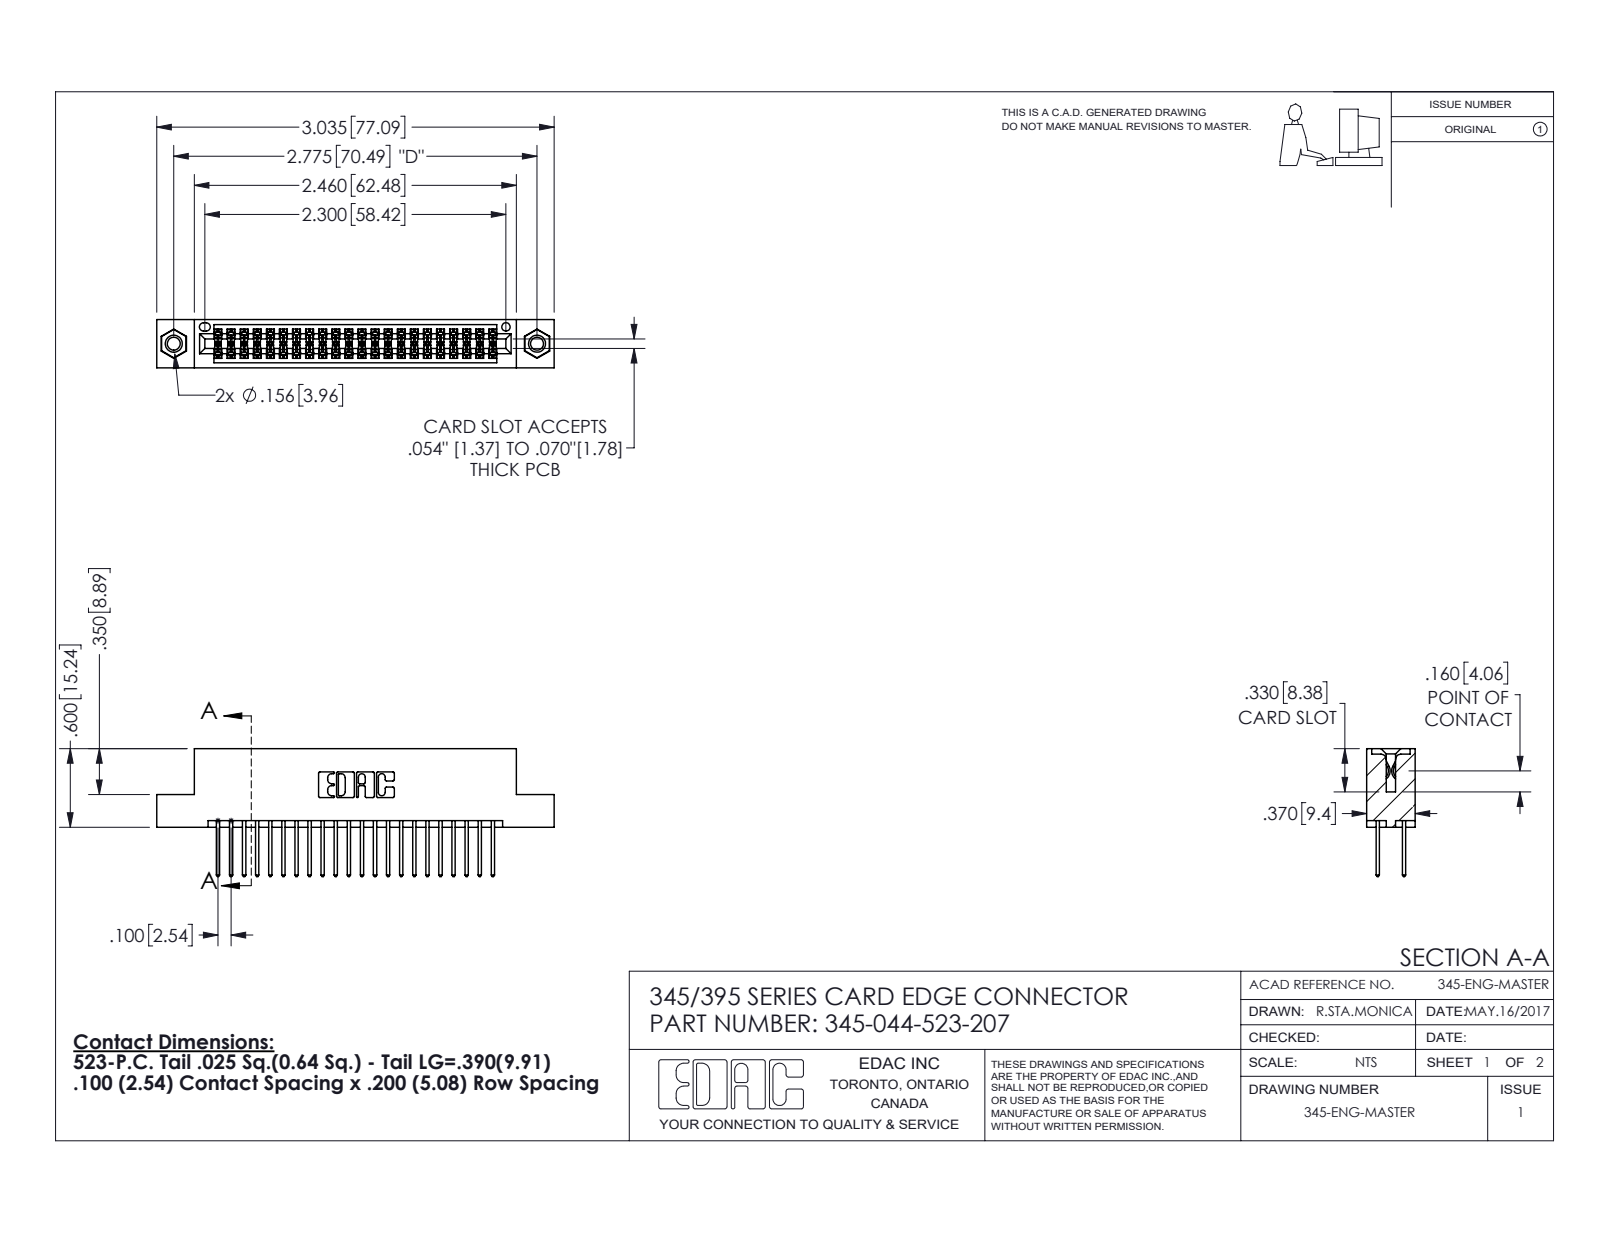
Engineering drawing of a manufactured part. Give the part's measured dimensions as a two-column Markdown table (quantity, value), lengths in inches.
| quantity | value |
| --- | --- |
| part name | 345 Part_Flush Mounting Lugs - 0.156 Dia-TI; 345-044-523-207; 345-292-001_345-293-123; 345-250-001_345-250-005-103 |
| STEP written by | SolidWorks 2016 (CONFIG_CONTROL_DESIGN) |
| units | inches |
| bodies | 47 solids, 2386 faces (1564 planar, 806 cylindrical, 16 other) |
| overall size | 3.035 × 0.977 × 0.37 |
| volume | 0.45 in³ |
| surface area | 16.98 in² |
| round holes (diameter × count) | 0.098 × 2, 0.125 × 2, 0.156 × 2, 0.064 × 1 |
| round bosses / shafts (diameter × count) | 0.155 × 2 |
| partial cylindrical surfaces (radius × count) | 0.006 × 66, 0.01 × 44, 0.01 × 22, 0.007 × 6, 0.031 × 6, 0.026 × 3, 0.014 × 2, 0.019 × 2 |
| main face-to-face distances | 0.072, 0.298, 0.2, 0.098, 0.272, 0.025, 0.37, 0.225, 0.175, 0.149 |
| hole center spacings | 0.27, 2.541, 2.775 |
